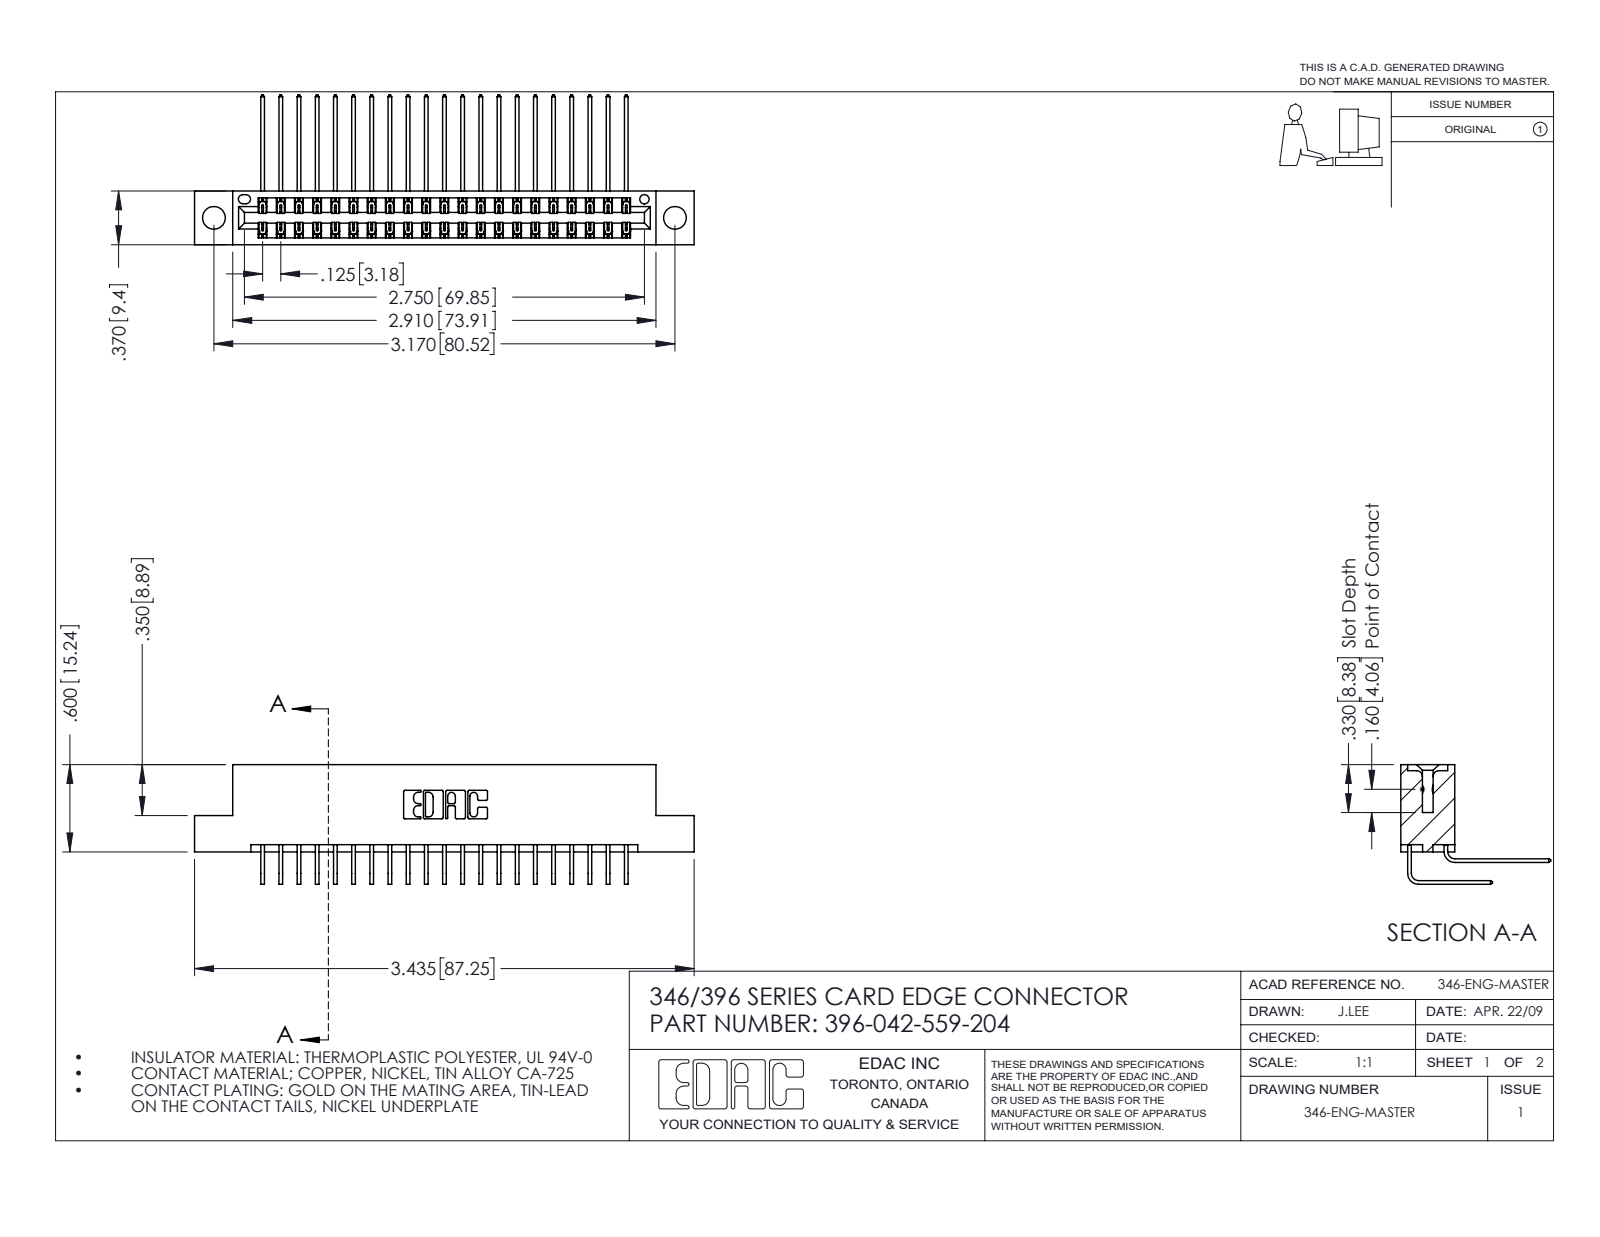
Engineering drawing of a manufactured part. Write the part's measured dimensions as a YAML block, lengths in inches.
part_name: "345-292-001_559 Tail - 2; 345-292-001_558 559 Tail - 1; 396-042-559-204; 346 Part_Flush Mounting Lugs - 0.156 Dia-TH"
step_written_by: "SolidWorks 2016 (CONFIG_CONTROL_DESIGN)"
units: inches
bodies: {solids: 43, faces: 2390, planar: 1630, cylindrical: 760, other: 0}
overall_size: [3.435, 1.03, 0.823]
volume: 0.519
surface_area: 19.11
round_holes:
  - {diameter: 0.156, count: 2}
  - {diameter: 0.064, count: 1}
partial_cylinders:
  - {radius: 0.006, count: 63}
  - {radius: 0.01, count: 22}
  - {radius: 0.007, count: 6}
  - {radius: 0.031, count: 6}
  - {radius: 0.026, count: 3}
  - {radius: 0.014, count: 2}
  - {radius: 0.022, count: 2}
  - {radius: 0.024, count: 2}
face_to_face_distances: [0.048, 0.322, 0.25, 0.025, 0.37, 0.072, 0.298, 0.275, 0.148, 0.222]
hole_center_spacings: [0.246, 2.963, 3.17]
